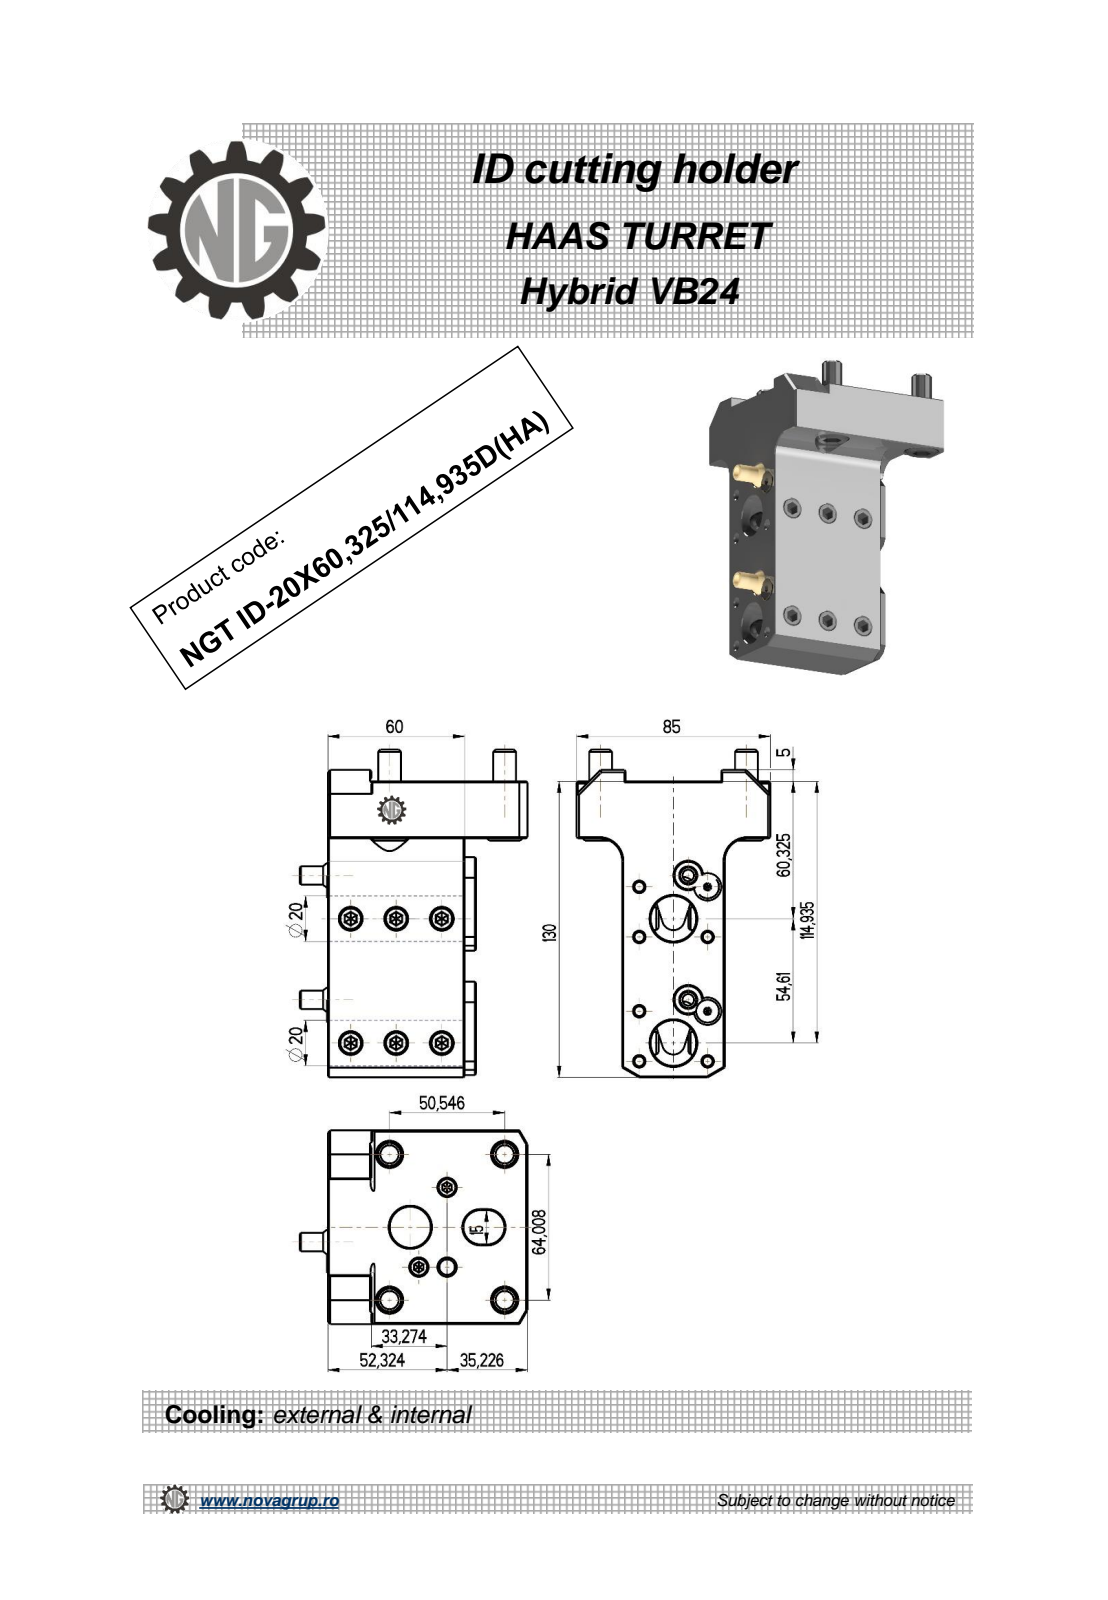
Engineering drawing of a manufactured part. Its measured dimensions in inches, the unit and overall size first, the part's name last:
Units: inches
Overall size (bounding box): 5.669 × 3.933 × 3.346
Round holes (diameter × count): ⌀0.197 ×2, ⌀0.787 ×2, ⌀0.268 ×1, ⌀0.709 ×1
Round bosses / shafts (diameter × count): ⌀0.394 ×12, ⌀0.315 ×2
Partial cylindrical surfaces — rounded edges, fillets, slot ends (radius × count): R0.02 ×60, R0.013 ×20, R0.008 ×12, R0.016 ×6, R0.197 ×6, R0.394 ×4, R0.295 ×2
Main face-to-face distances: 2.559, 1.772, 0.787, 0.197, 2.362, 3.346, 5.118, 4.134, 0.984, 0.888
Hole centre spacings: 0.791, 2.15, 0.938, 1.425, 2.909
Volume: 27.13 in³ · Surface area: 93.69 in²
Bodies: 1 solid, 676 faces (300 planar, 176 cylindrical, 200 other)
Part name (STEP PRODUCT): NGT_ID_20_60_325_114_935D_HA
STEP written by: PRO/ENGINEER BY PARAMETRIC TECHNOLOGY CORPORATION, 2010280 (CONFIG_CONTROL_DESIGN)
